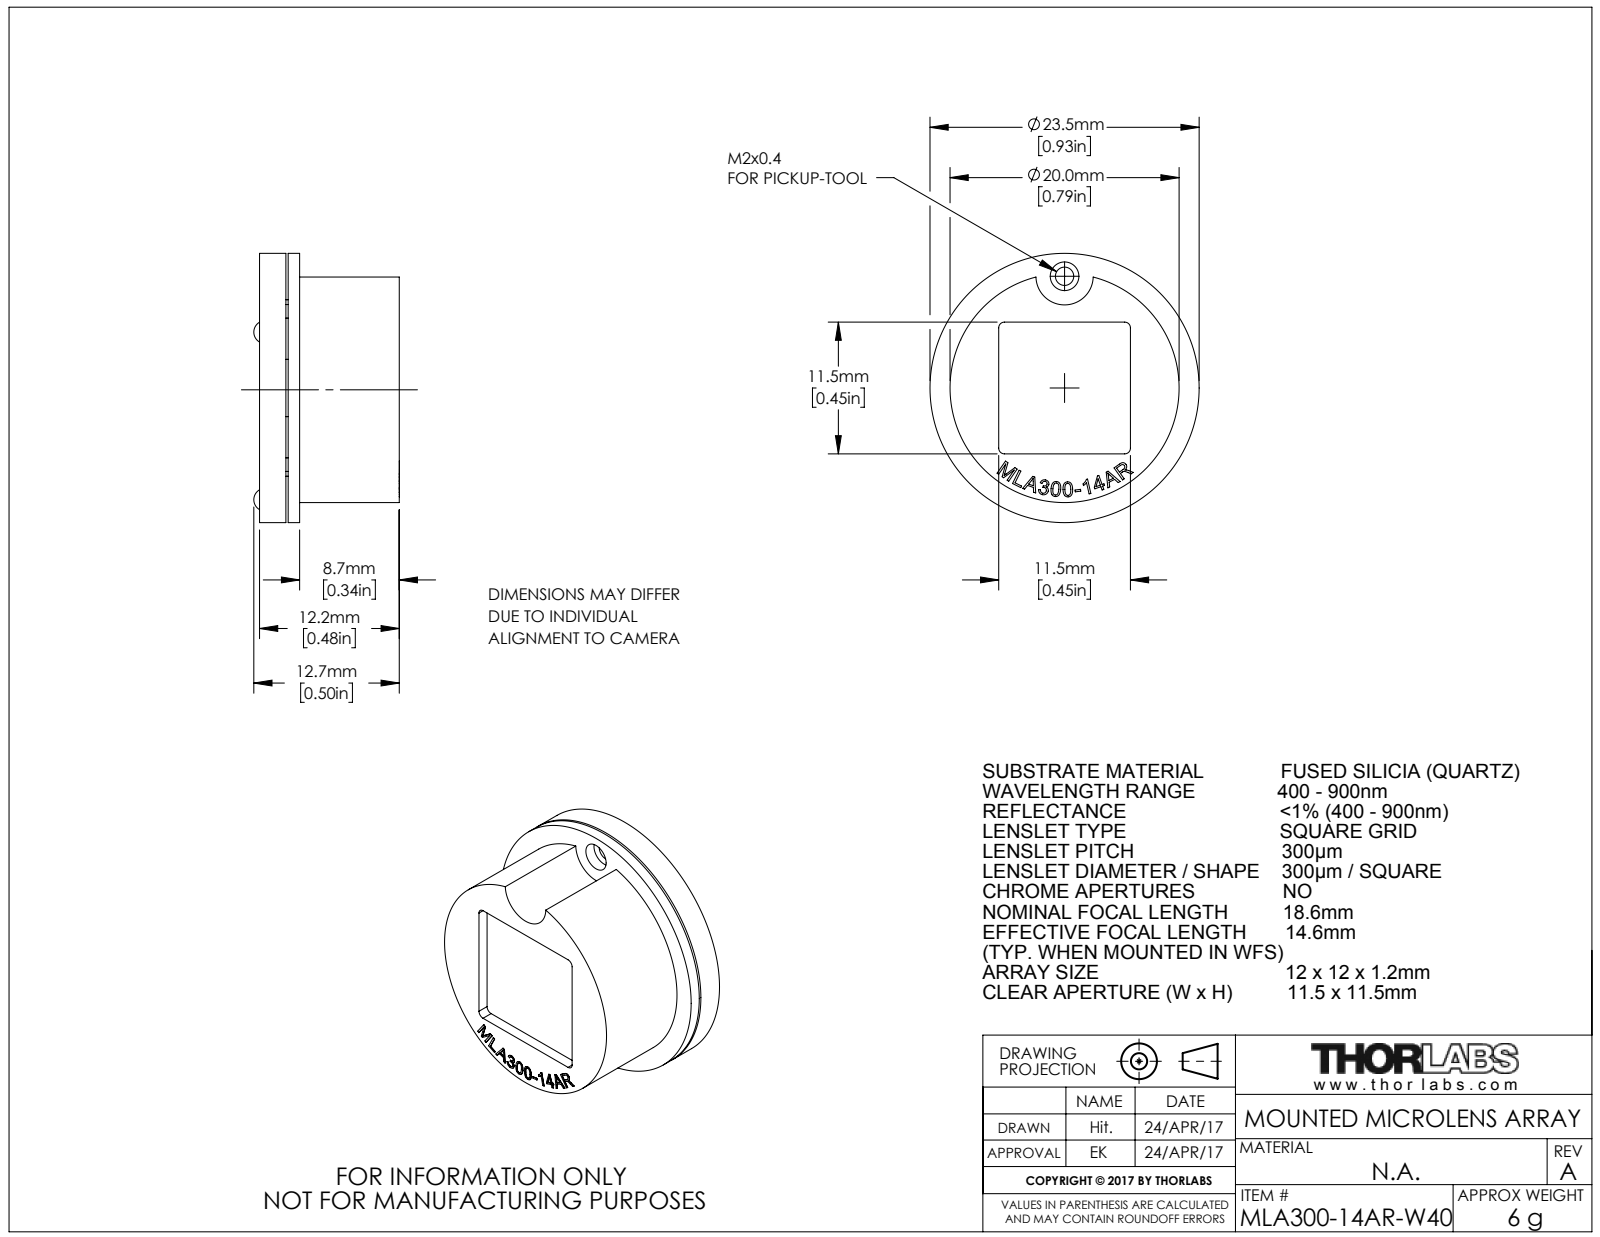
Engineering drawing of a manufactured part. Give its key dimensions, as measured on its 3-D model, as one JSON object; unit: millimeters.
{"part_name": "MTN009306-E0W", "step_written_by": "SolidWorks 2016 (AUTOMOTIVE_DESIGN)", "units": "millimeters", "bodies": {"solids": 12, "faces": 295, "planar": 169, "cylindrical": 70, "other": 56}, "overall_size": [23.5, 23.5, 12.71], "volume_mm3": 2201, "surface_area_mm2": 3212, "round_holes": [[3.2, 6], [1.9, 3], [1.5, 1], [1.6, 1], [2.5, 1]], "round_bosses_or_shafts": [[3, 6], [23.5, 1], [20, 1]], "partial_cylinders_radius": [[0.5, 8], [2.5, 5], [7.7, 1], [7.75, 1]], "face_to_face_distances": [1, 1.2, 8.7, 8.9, 7.7, 12.2, 9.9, 9.7, 2.2, 11.2], "hole_center_spacings": [18.83, 13.79, 16.88, 5.04, 5.05, 9.74, 16.89, 9.75]}
